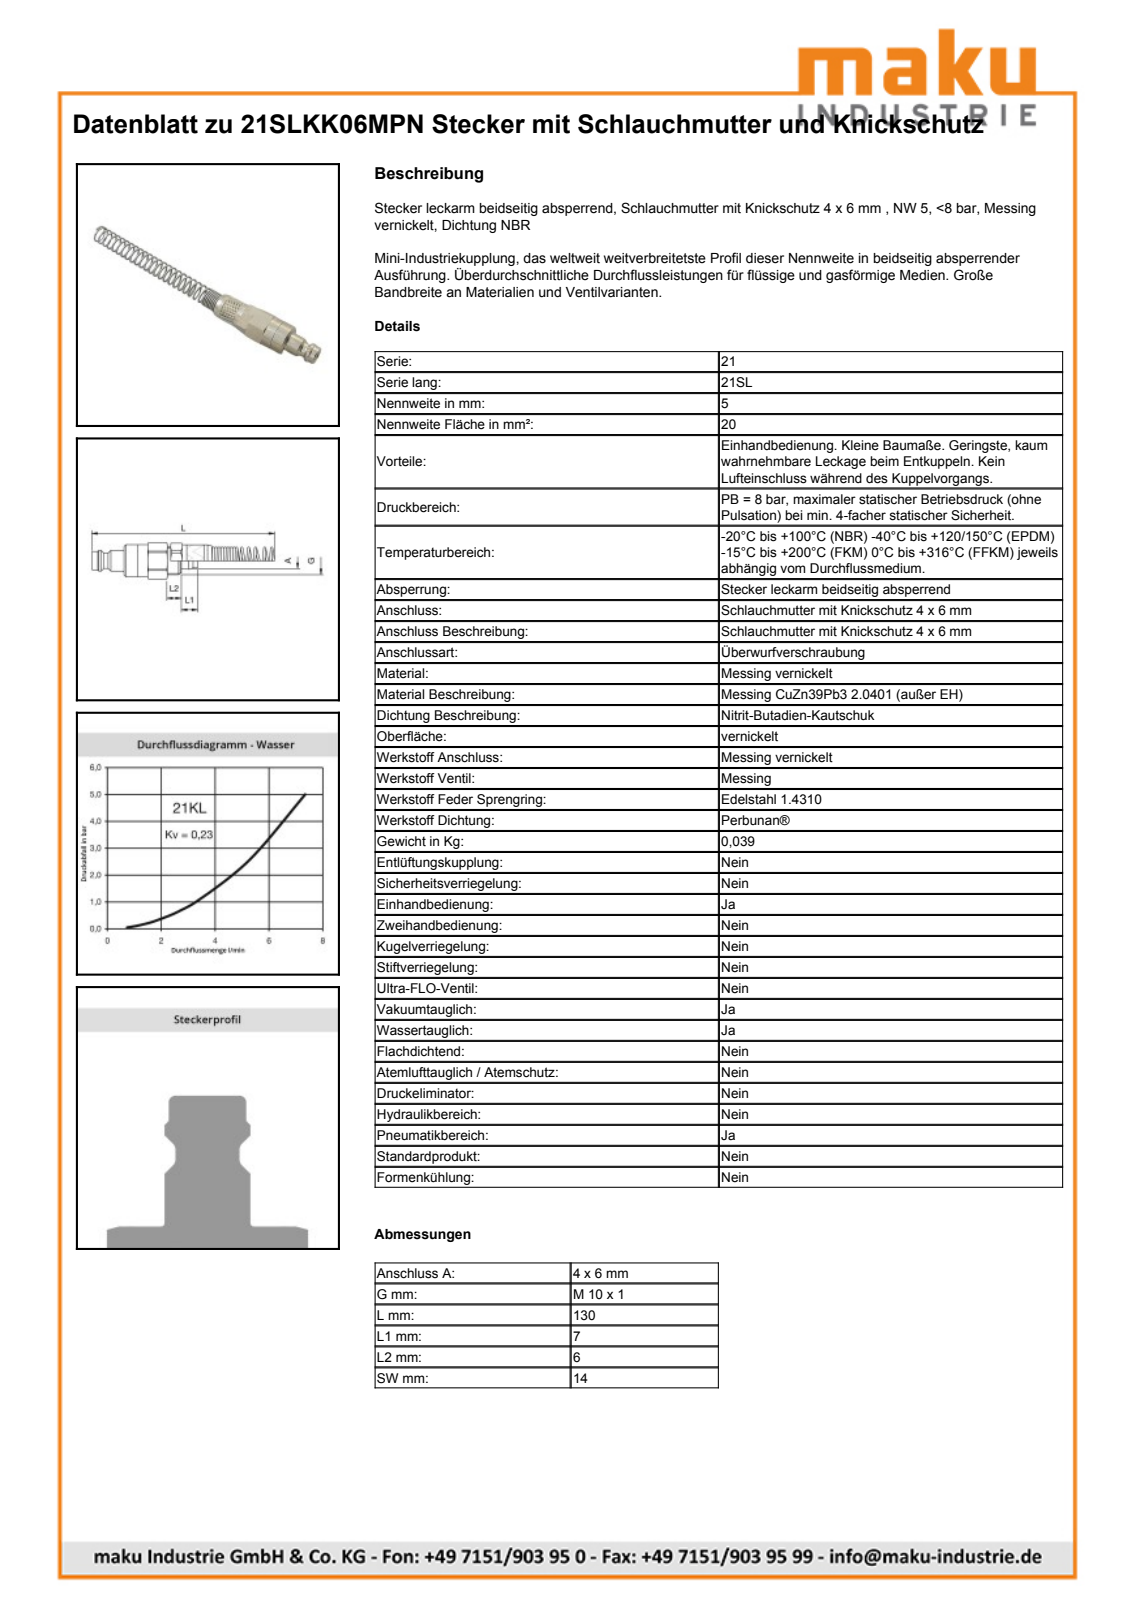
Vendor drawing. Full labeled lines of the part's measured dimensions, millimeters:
Part name (STEP PRODUCT): D104660; D102680; D104658; D104659 (+1 more)
STEP written by: Autodesk Inventor 2011 (AUTOMOTIVE_DESIGN)
Units: millimetres
Bodies: 4 solids, 121 faces (30 planar, 37 cylindrical, 54 other)
Overall size (bounding box): 125.08 × 15.8 × 14
Volume: 4 096 mm³ · Surface area: 7 487 mm²
Round holes (diameter × count): ⌀3 ×1, ⌀4.2 ×1, ⌀5.5 ×1, ⌀6.25 ×1, ⌀7.2 ×1, ⌀9.5 ×1, ⌀10 ×1, ⌀10.45 ×1
Round bosses / shafts (diameter × count): ⌀14 ×1, ⌀12 ×1, ⌀11.98 ×1, ⌀11.9 ×1, ⌀11 ×1, ⌀9 ×1, ⌀8.6 ×1, ⌀8.1 ×1
Partial cylindrical surfaces — rounded edges, fillets, slot ends (radius × count): R6.7 ×1, R7.9 ×1
Main face-to-face distances: 14, 12, 11, 1.75, 12.75, 7, 9.75, 5.9, 16.9, 18.65
